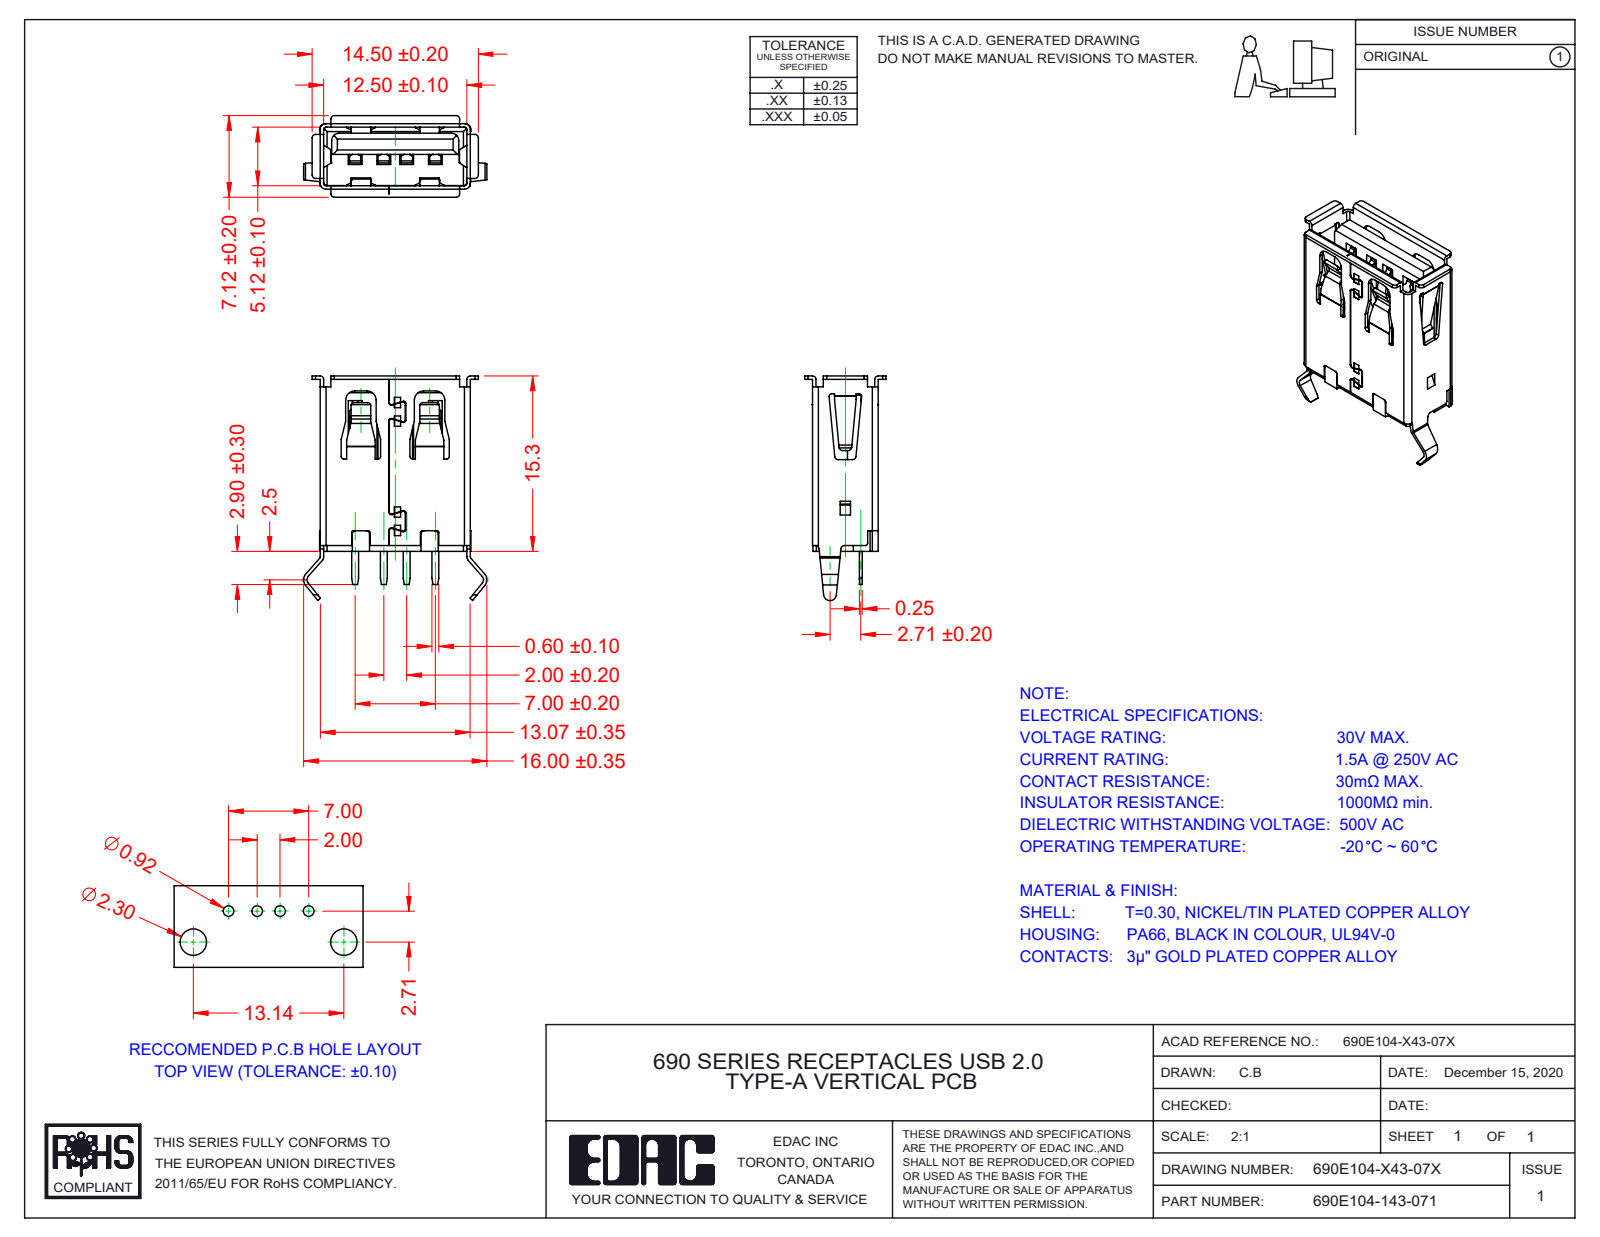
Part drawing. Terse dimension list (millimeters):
name: Shell 690E104-X43-07X; 690E104-143-071; Contact 690E104-X43-07X; Insulator2 690E104-X43-07X_Black (+1 more)
written by: SolidWorks 2020 (AUTOMOTIVE_DESIGN)
unit: mm
bodies: 7 solids, 806 faces (597 planar, 209 cylindrical, 0 other)
size: 19.6 × 16 × 7.12
volume: 609 mm³; area: 2 267 mm²
rounds: 37× R0.2, 30× R0.3, 25× R0.15, 15× R0.5, 9× R0.25, 6× R0.8, 4× R0.24, 4× R0.62
face distances: 5.42, 5.12, 5.72, 12.8, 1.09, 2.5, 1.39, 1.2, 4.5, 4.03
